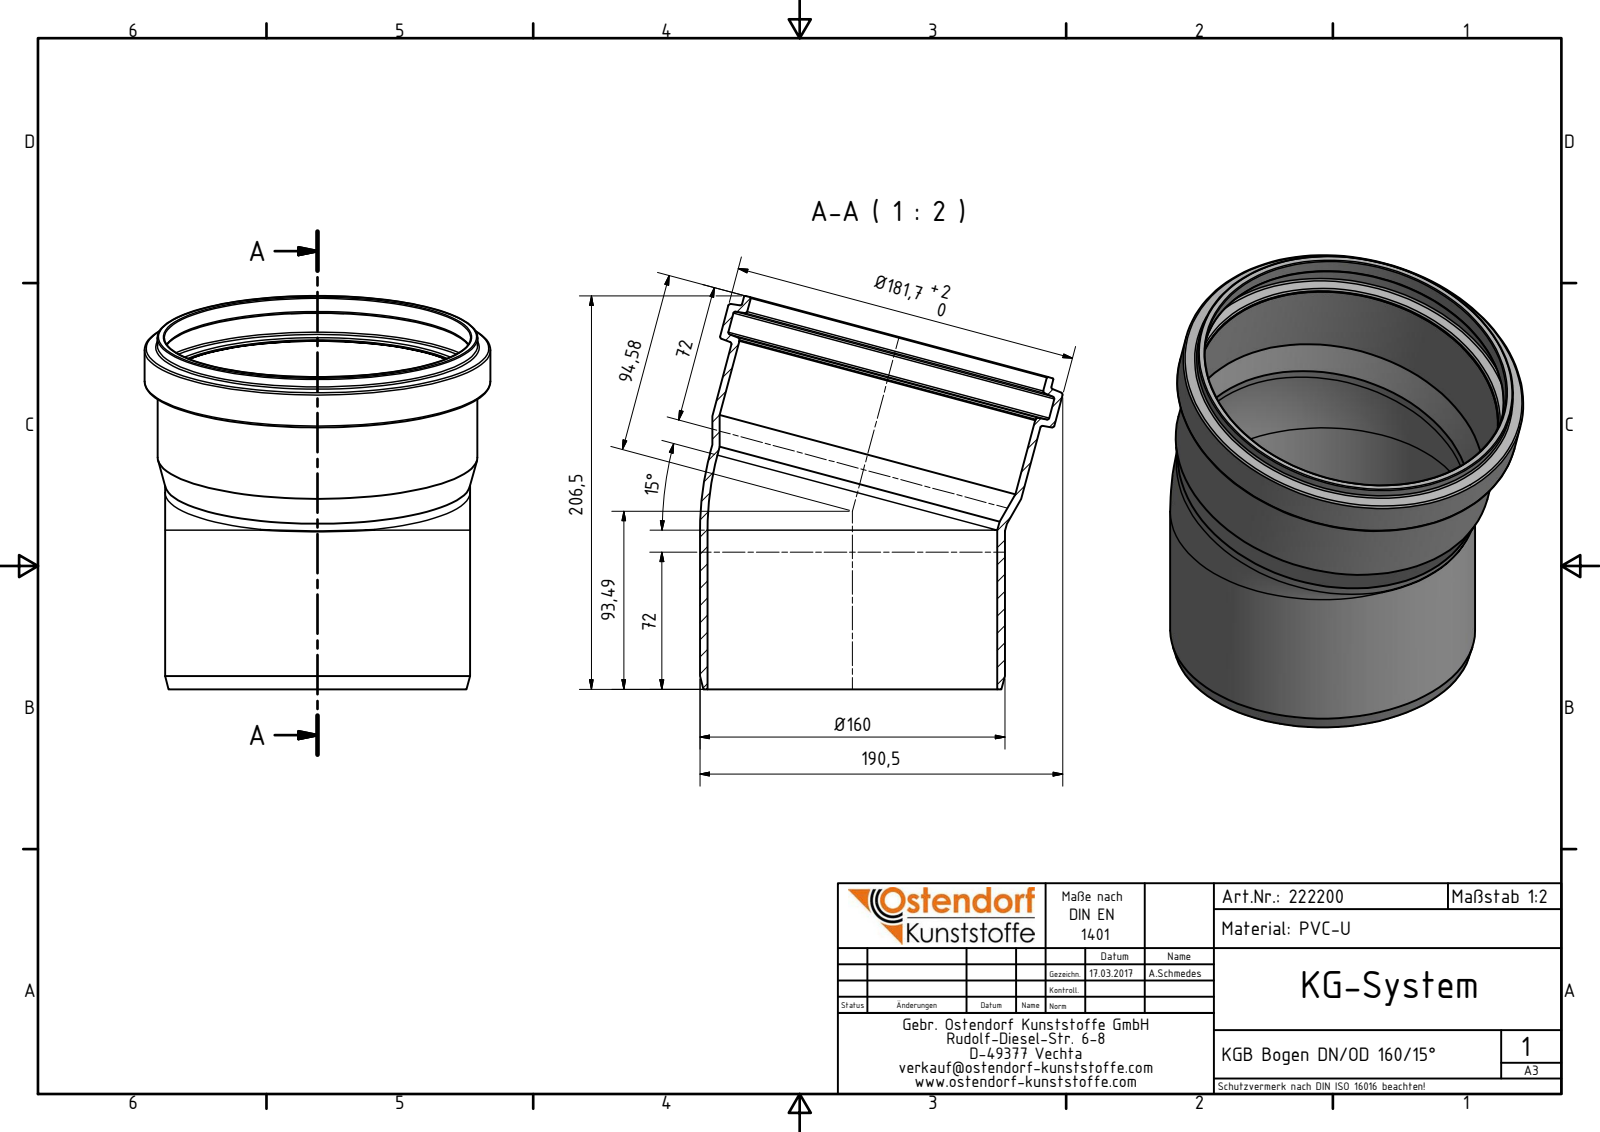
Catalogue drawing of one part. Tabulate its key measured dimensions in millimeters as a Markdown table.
| quantity | value |
| --- | --- |
| part name | 222200 KGB Bogen DN_OD 160_15° |
| STEP written by | Autodesk Inventor 2016 (AUTOMOTIVE_DESIGN) |
| units | millimeters |
| bodies | 1 solid, 34 faces (3 planar, 11 cylindrical, 20 other) |
| overall size | 206.5 × 190.5 × 181.7 |
| volume | 381 429 mm³ |
| surface area | 204 644 mm² |
| round holes (diameter × count) | 152.15 × 2, 161 × 2, 160.75 × 1, 174.5 × 1 |
| round bosses / shafts (diameter × count) | 160.15 × 2, 181.7 × 1, 168.2 × 1, 167.95 × 1 |
| main face-to-face distances | 23.61 |
